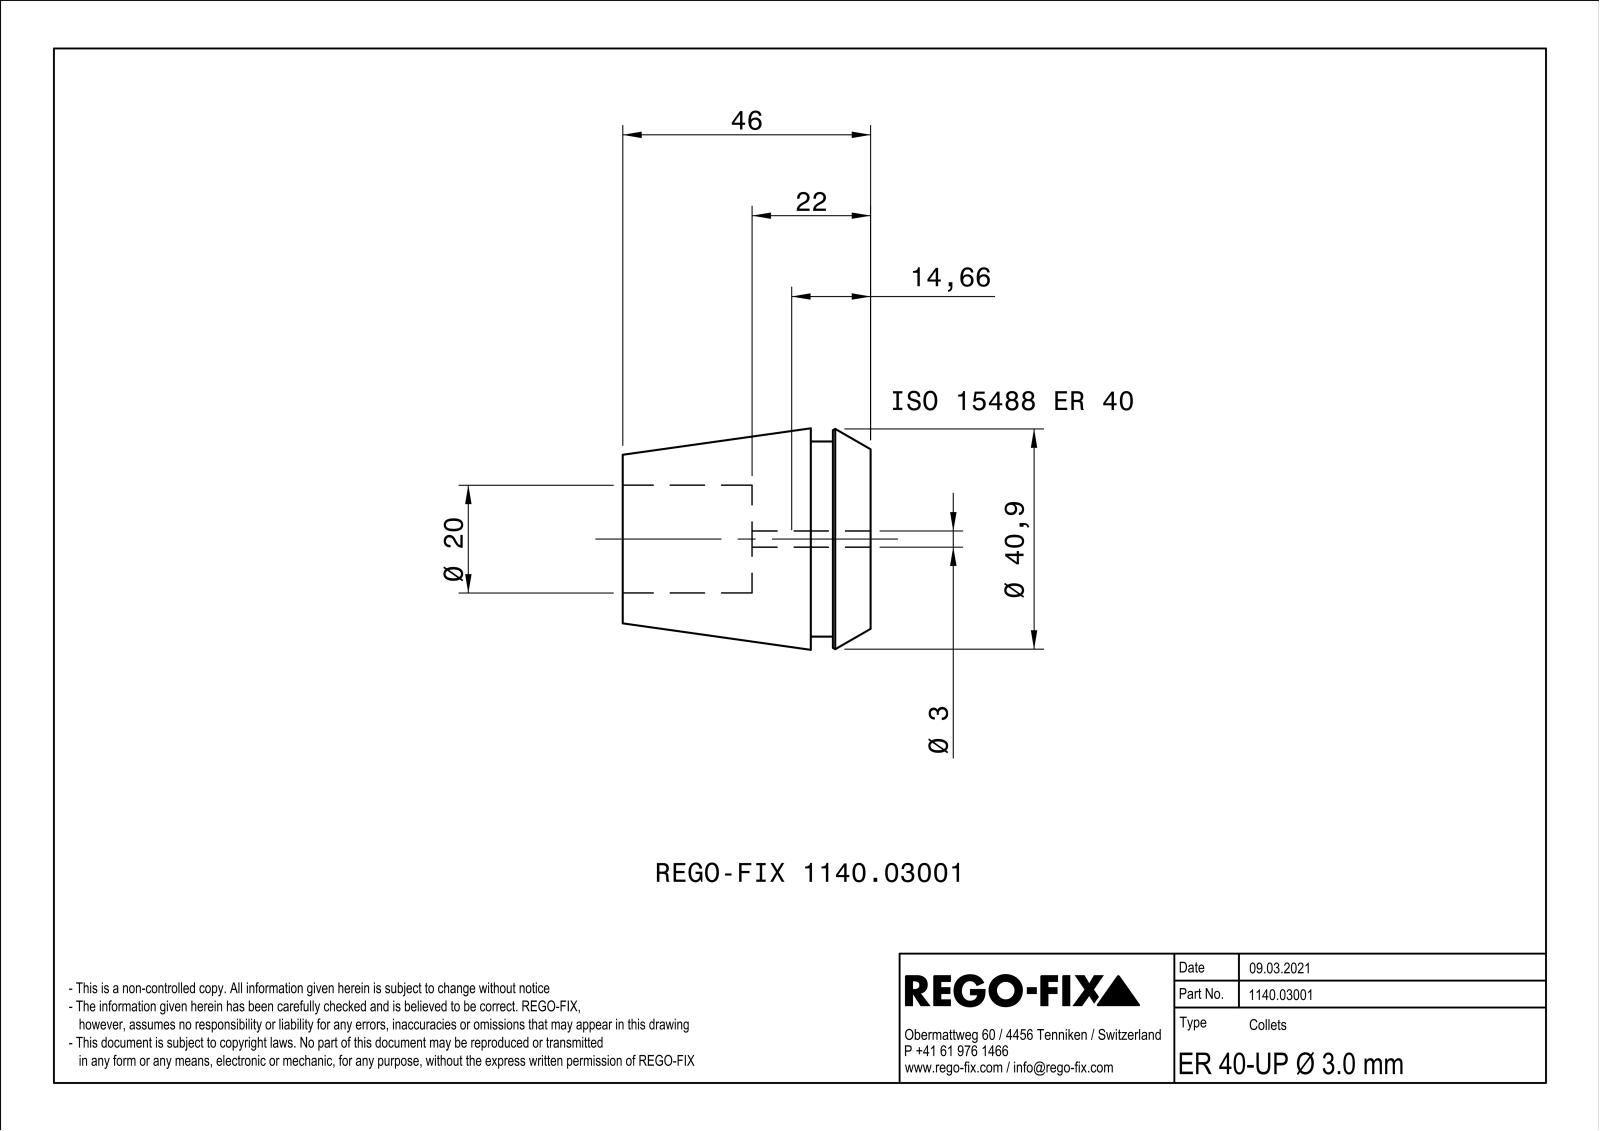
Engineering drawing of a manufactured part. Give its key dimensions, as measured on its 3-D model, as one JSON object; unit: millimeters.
{"part_name": "NOCUT", "step_written_by": "SIEMENS PLM Software Solid Edge ST10 (AUTOMOTIVE_DESIGN)", "units": "millimeters", "bodies": {"solids": 1, "faces": 272, "planar": 104, "cylindrical": 48, "other": 120}, "overall_size": [46, 41.1, 41.1], "volume_mm3": 36331, "surface_area_mm2": 21663, "round_holes": [[20, 1]], "round_bosses_or_shafts": [[36.2, 1]], "partial_cylinders_radius": [[45, 8], [1.5, 1]], "face_to_face_distances": [0.6, 0.58, 0.62, 46, 11.1, 34.9, 22, 10.9, 24, 7]}
